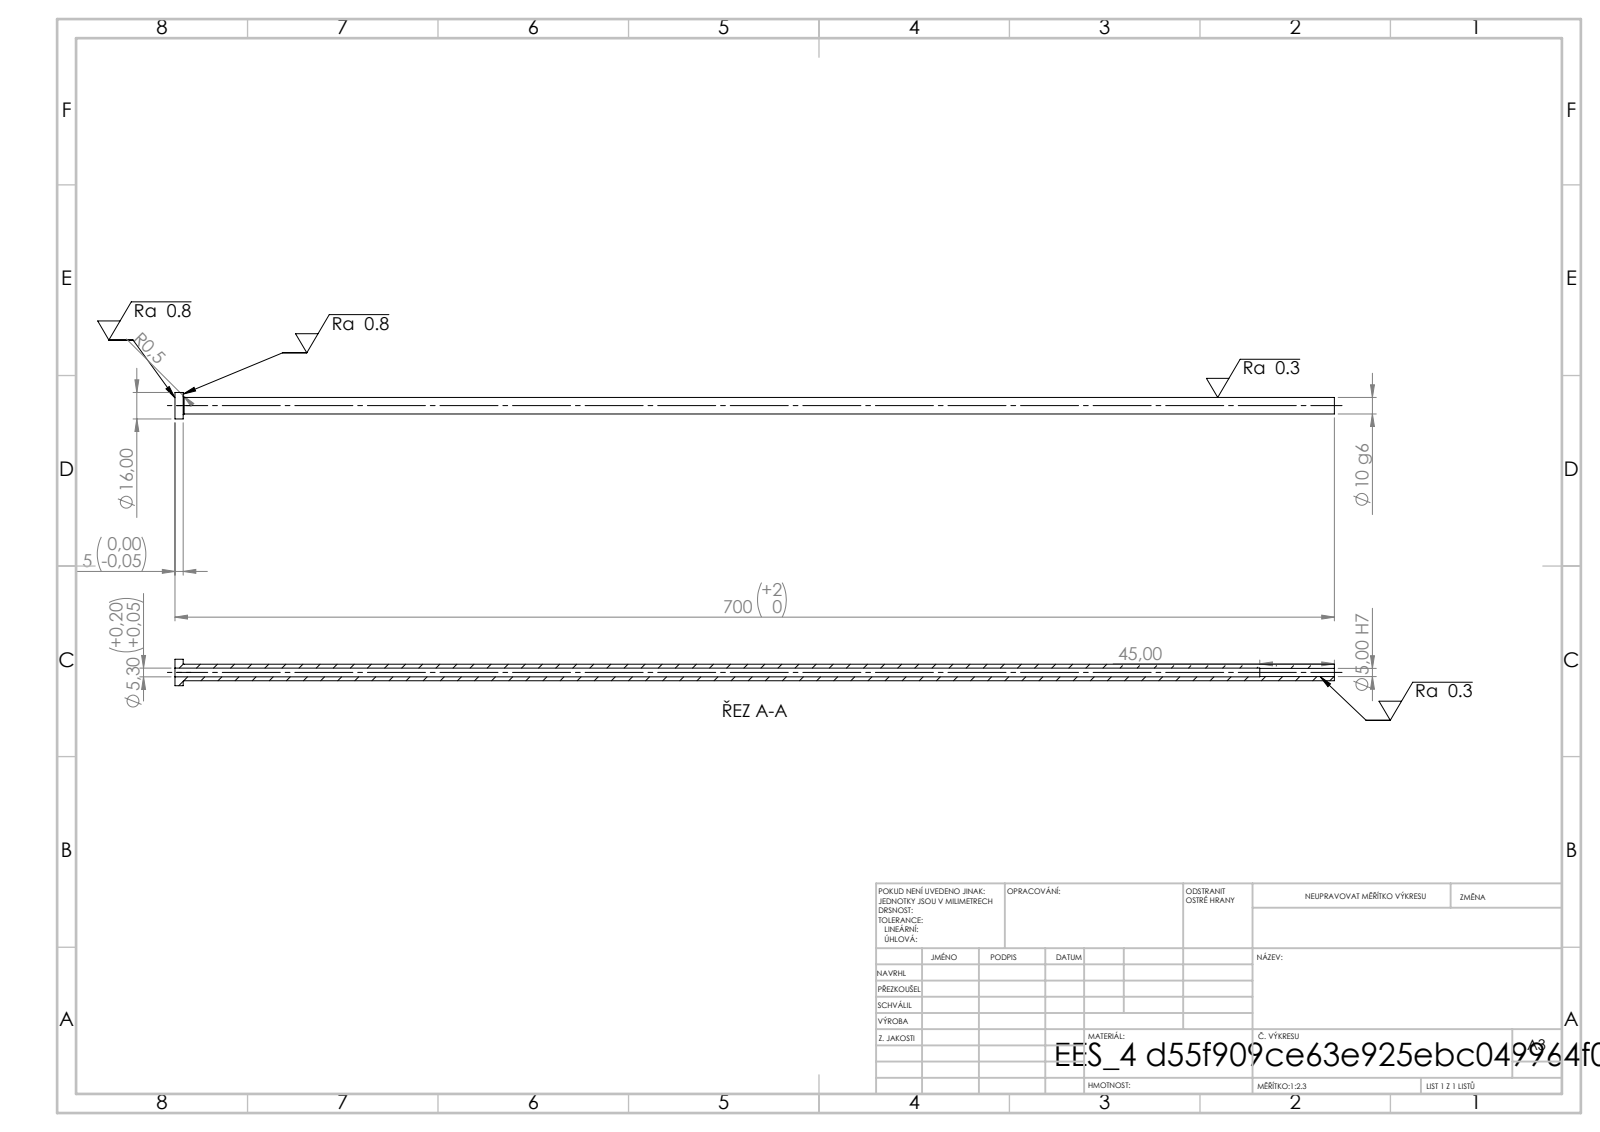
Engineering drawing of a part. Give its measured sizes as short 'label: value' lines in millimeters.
written by: SolidWorks 2019 (CONFIG_CONTROL_DESIGN)
unit: mm
bodies: 1 solid, 14 faces (4 planar, 8 cylindrical, 2 other)
size: 700 × 16 × 16
volume: 40 258 mm³; area: 34 055 mm²
holes: 1× ⌀5, 1× ⌀5.3
bosses: 1× ⌀16, 1× ⌀10
face distances: 5, 700, 695, 655, 650, 45
